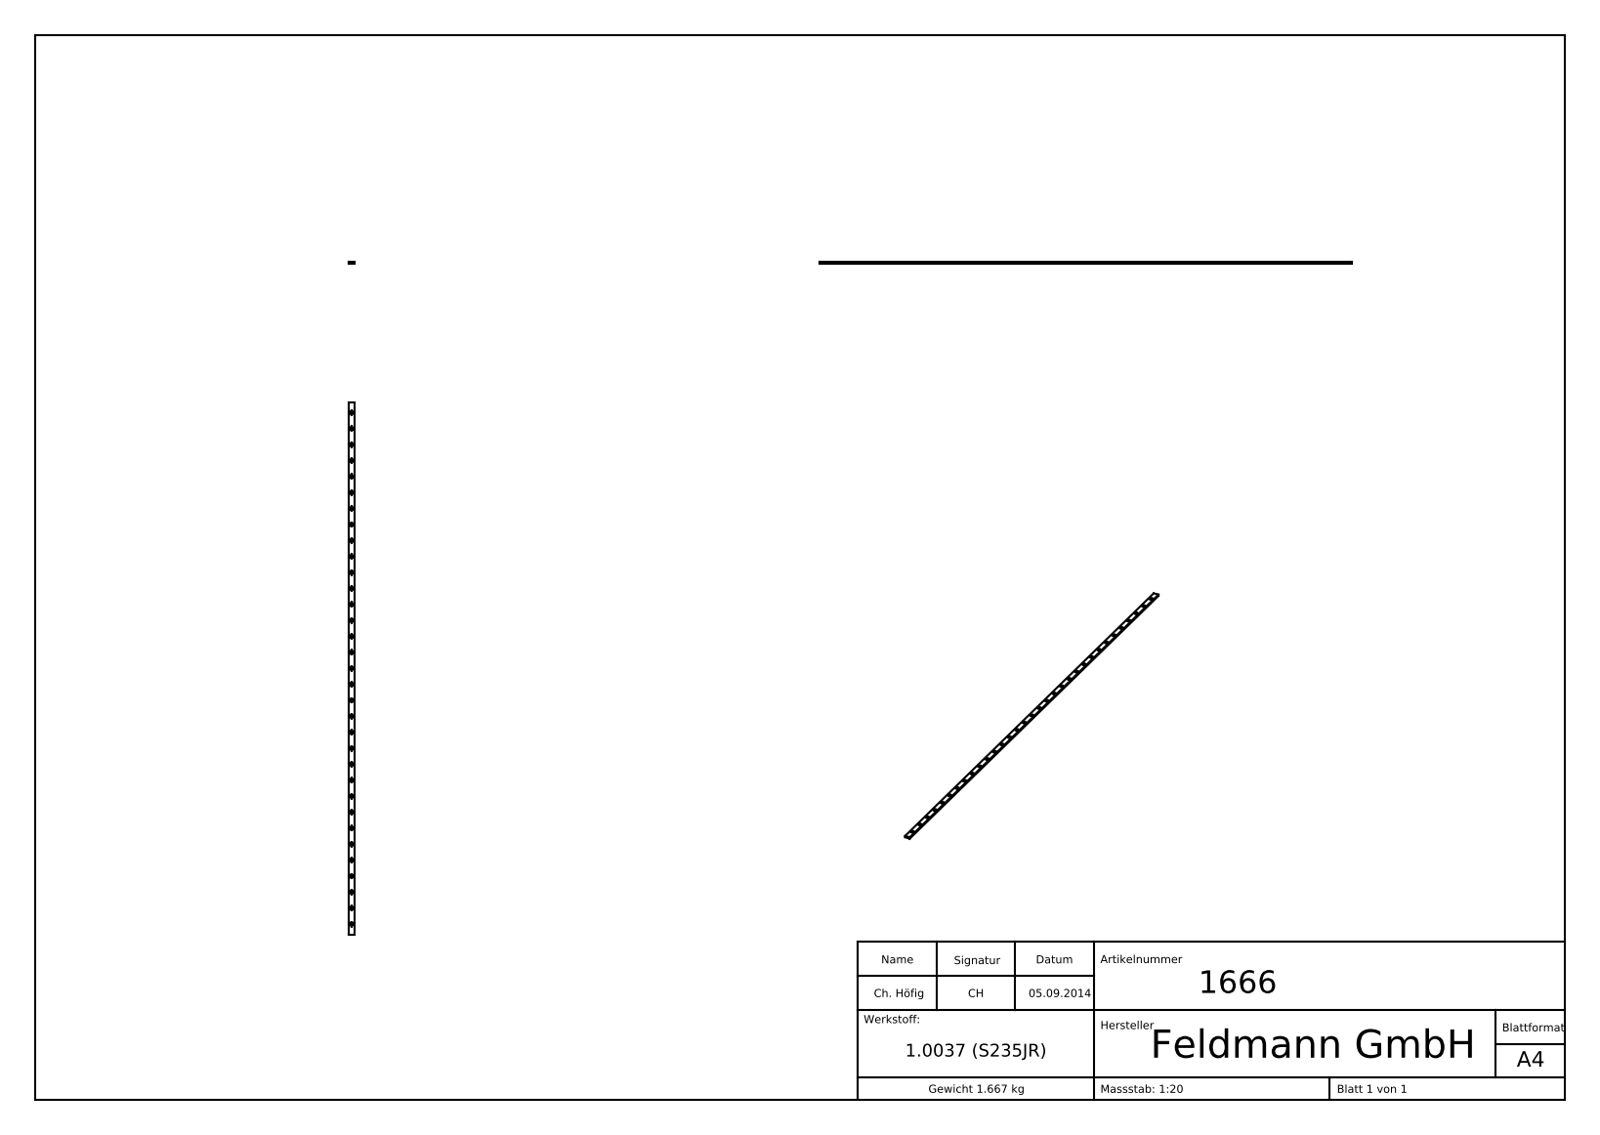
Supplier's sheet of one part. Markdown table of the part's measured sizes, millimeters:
| quantity | value |
| --- | --- |
| part name | 1666 |
| STEP written by | SolidWorks 2015 (CONFIG_CONTROL_DESIGN) |
| units | millimeters |
| bodies | 1 solid, 185 faces (71 planar, 66 cylindrical, 48 other) |
| overall size | 2000 × 20 × 6 |
| volume | 213 718 mm³ |
| surface area | 103 590 mm² |
| round holes (diameter × count) | 13 × 33 |
| main face-to-face distances | 6, 20, 2000, 0.5, 1999.5, 2.97, 0.39, 1.12, 3.66, 4.23 |
| hole center spacings | 60, 120, 180, 240, 300, 360, 420, 480 |
